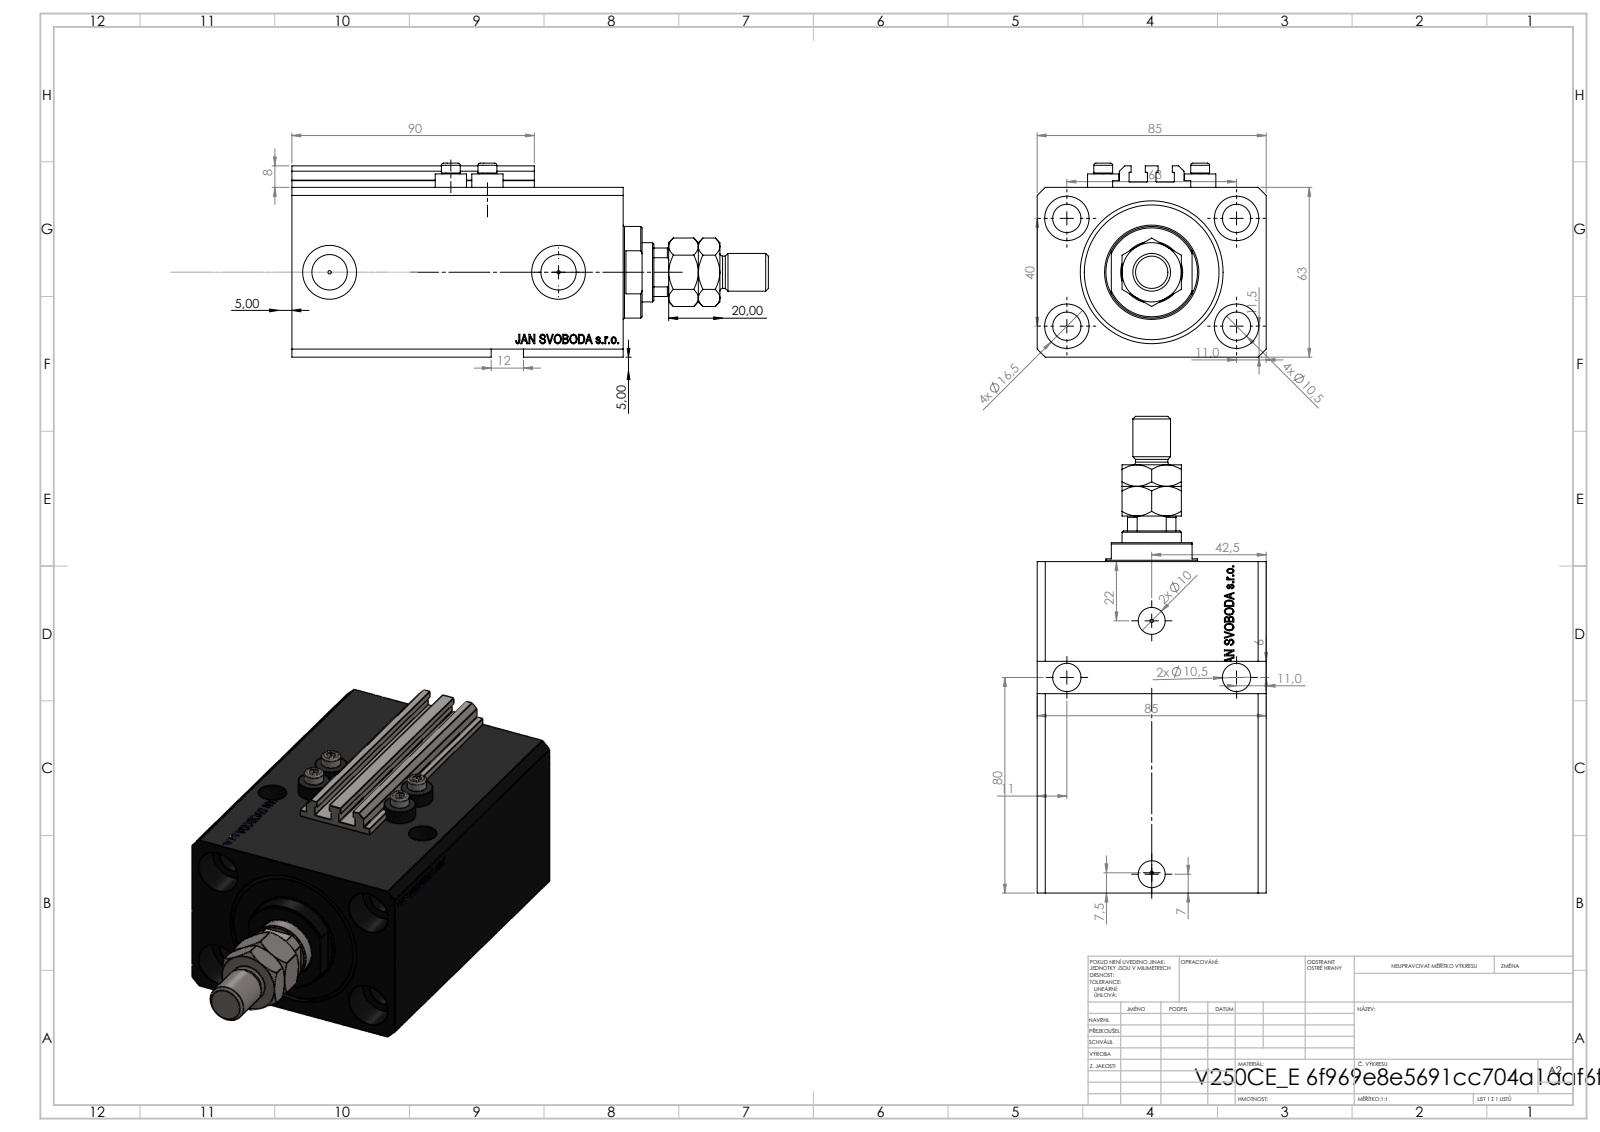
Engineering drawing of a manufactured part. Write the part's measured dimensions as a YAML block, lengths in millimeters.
part_name: "V250CE_E_Body; V250CE_VC_E; V250CE_C_VCP; MTA (+1 more)"
step_written_by: "SolidWorks 2019 (CONFIG_CONTROL_DESIGN)"
units: millimeters
bodies: {solids: 9, faces: 1156, planar: 550, cylindrical: 150, other: 456}
overall_size: [177, 85, 72]
volume: 567178
surface_area: 122369
round_holes:
  - {diameter: 10.5, count: 8}
  - {diameter: 1.25, count: 4}
  - {diameter: 4, count: 4}
  - {diameter: 16.5, count: 4}
  - {diameter: 10, count: 2}
  - {diameter: 13.16, count: 2}
  - {diameter: 20, count: 2}
  - {diameter: 12.5, count: 1}
  - {diameter: 22, count: 1}
  - {diameter: 40, count: 1}
  - {diameter: 53, count: 1}
round_bosses_or_shafts:
  - {diameter: 11.6, count: 4}
  - {diameter: 7, count: 4}
  - {diameter: 34, count: 1}
  - {diameter: 14, count: 1}
  - {diameter: 12, count: 1}
partial_cylinders:
  - {radius: 0.2, count: 10}
  - {radius: 10.5, count: 1}
face_to_face_distances: [63, 85, 17, 123, 106, 11.4, 94.6, 111.6, 3, 65]
hole_center_spacings: [37.31, 63, 13.6, 15.4, 24.96, 27.54, 33.62, 36]
